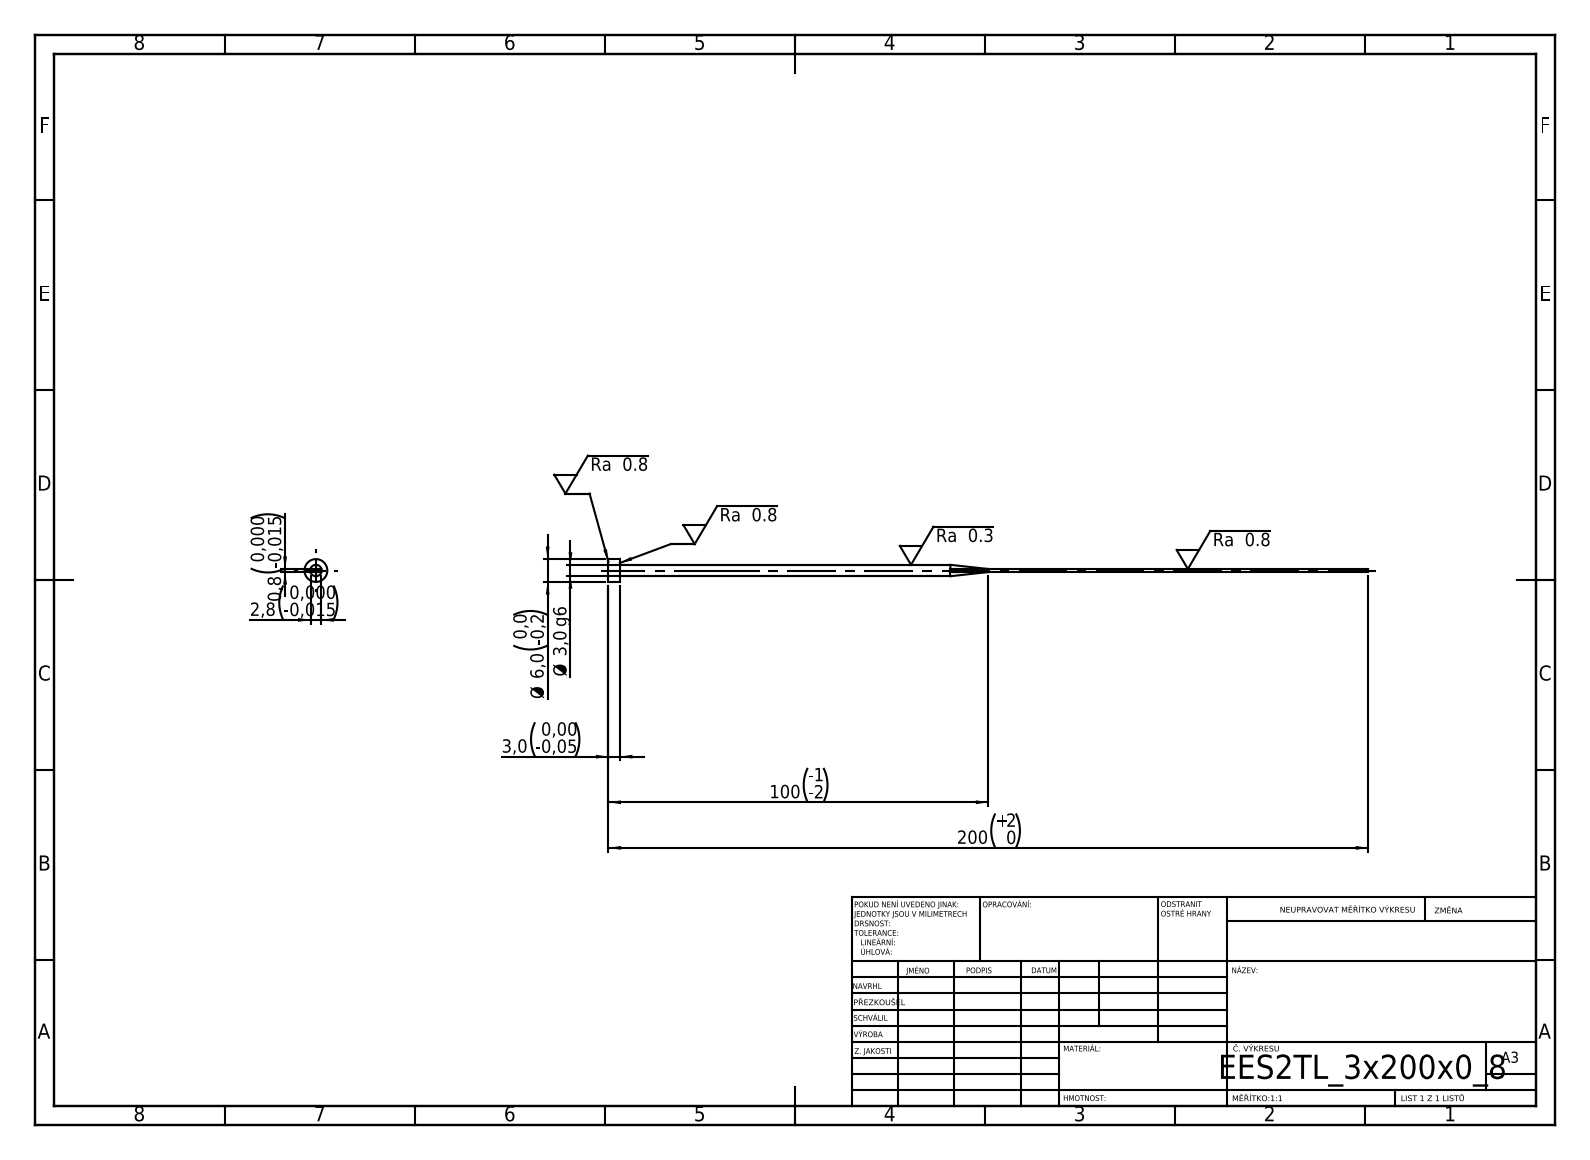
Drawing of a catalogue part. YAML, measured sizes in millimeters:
step_written_by: "SolidWorks 2019 (CONFIG_CONTROL_DESIGN)"
units: millimeters
bodies: {solids: 1, faces: 15, planar: 7, cylindrical: 4, other: 4}
overall_size: [200, 6, 6]
volume: 969
surface_area: 1728
round_bosses_or_shafts:
  - {diameter: 6, count: 1}
  - {diameter: 3, count: 1}
face_to_face_distances: [0.8, 2.8, 3, 200, 197]
